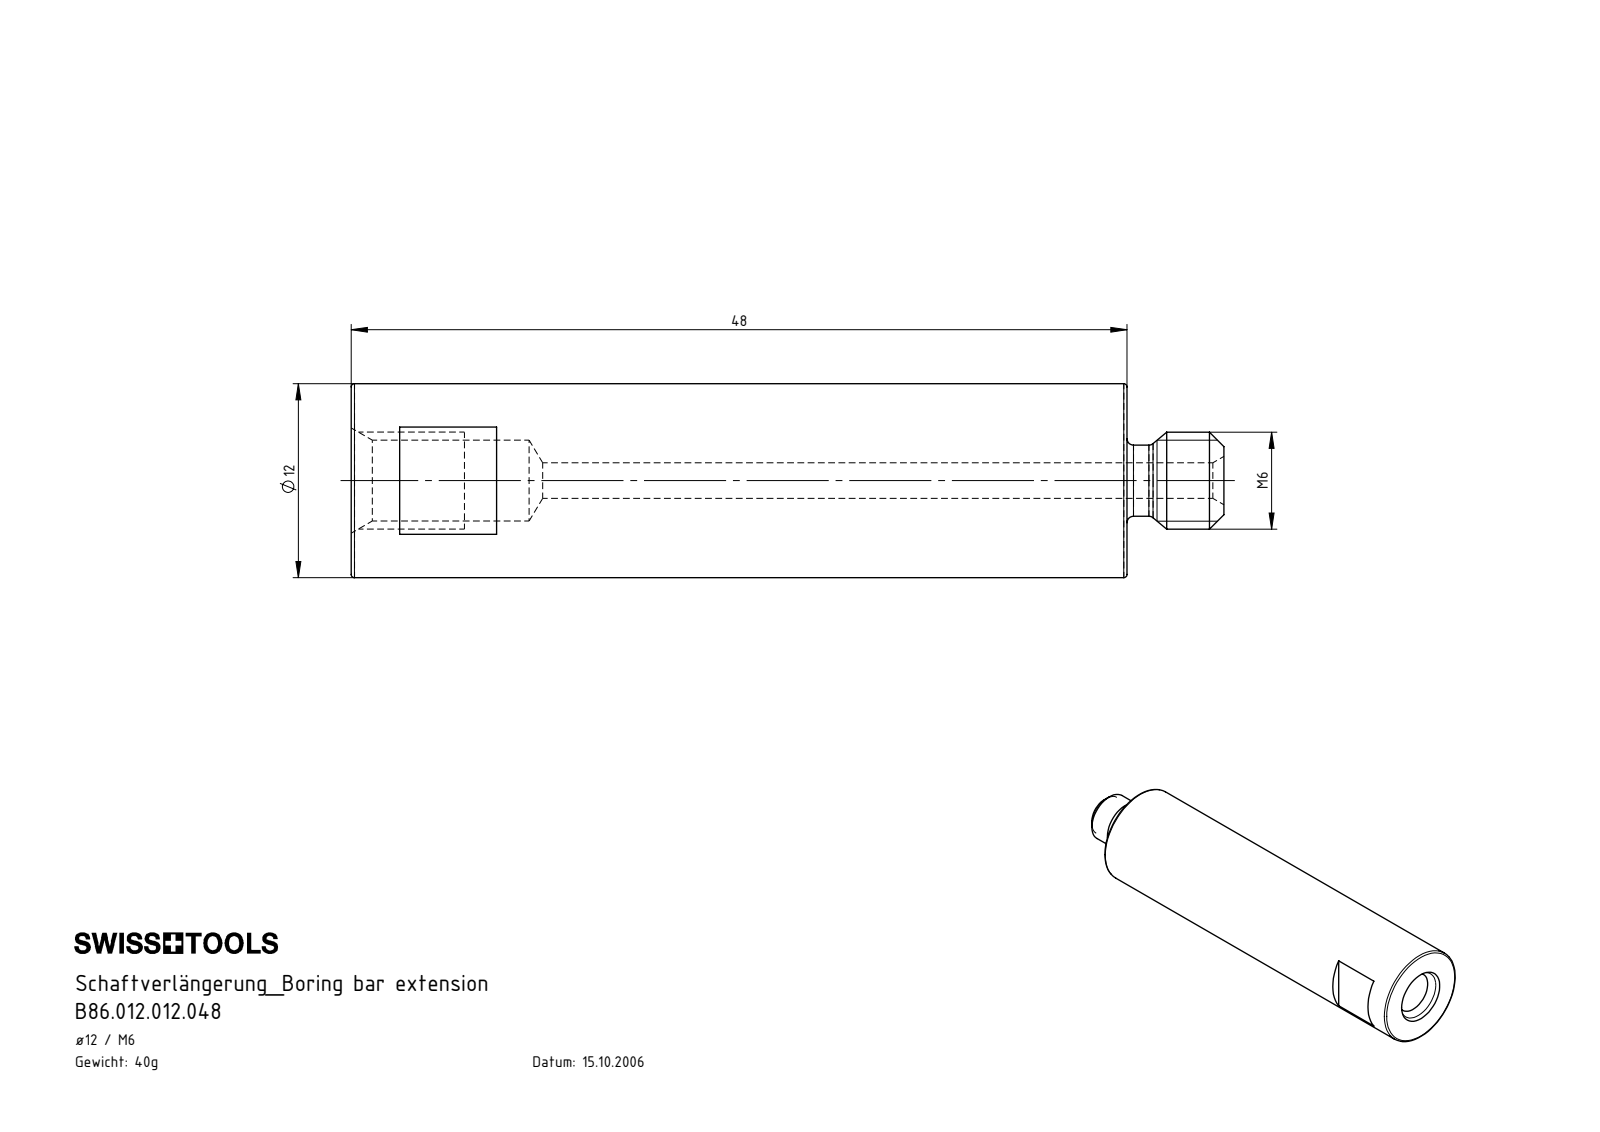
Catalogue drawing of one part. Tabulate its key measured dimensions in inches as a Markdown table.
| quantity | value |
| --- | --- |
| part name | B86.012.012.048 |
| STEP written by | SolidWorks 2022 (CONFIG_CONTROL_DESIGN) |
| units | inches |
| bodies | 1 solid, 37 faces (9 planar, 10 cylindrical, 18 other) |
| overall size | 2.126 × 0.472 × 0.472 |
| volume | 0.312 in³ |
| surface area | 4.032 in² |
| round holes (diameter × count) | 0.087 × 1, 0.197 × 1 |
| round bosses / shafts (diameter × count) | 0.472 × 1, 0.236 × 1, 0.173 × 1 |
| main face-to-face distances | 1.89, 0.394, 1.772, 0.236, 0.118, 1.535, 0.354, 2.008, 2.126 |
